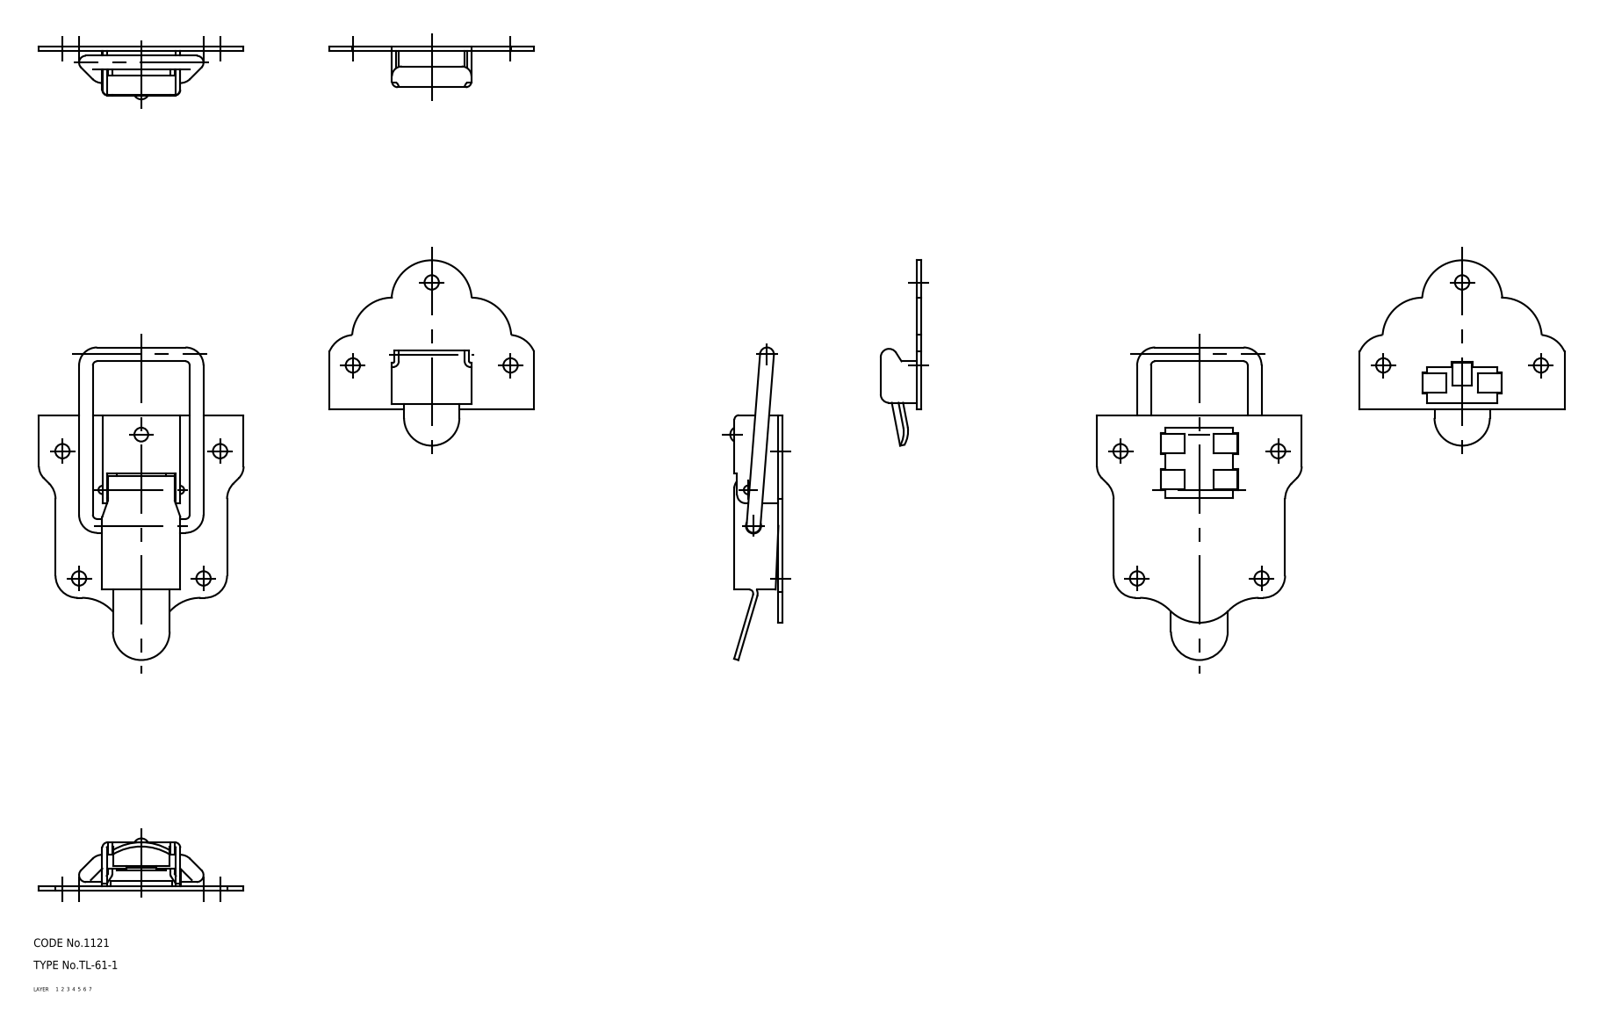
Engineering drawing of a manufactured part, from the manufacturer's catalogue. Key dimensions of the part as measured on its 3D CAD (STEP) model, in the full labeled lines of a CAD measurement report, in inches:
Part name (STEP PRODUCT): shaft; lever; keeper; base (+2 more)
STEP written by: CADfix (AUTOMOTIVE_DESIGN)
Units: inches
Bodies: 5 solids, 300 faces (0 planar, 0 cylindrical, 300 other)
Overall size (bounding box): 5.689 × 2.913 × 0.747
Volume: 1.557 in³ · Surface area: 50.19 in²
